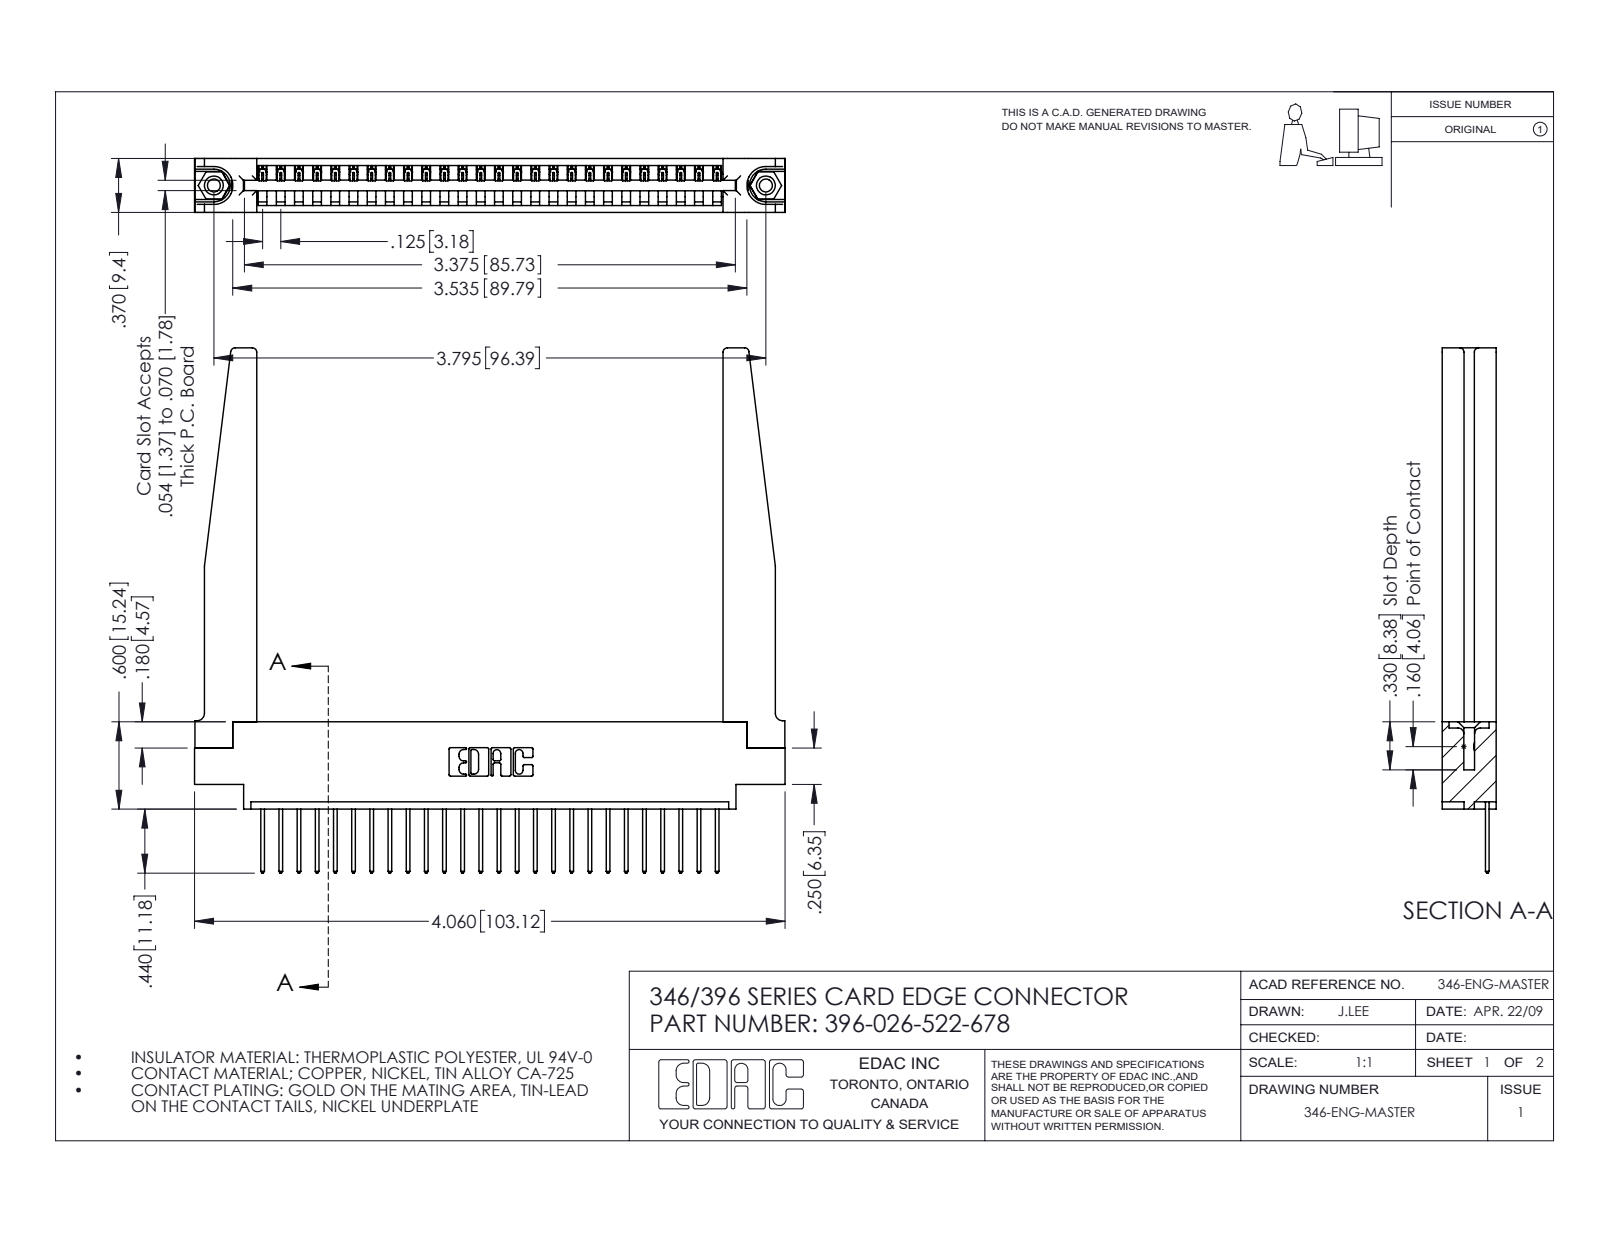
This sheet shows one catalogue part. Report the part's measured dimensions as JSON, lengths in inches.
{"part_name": "345-250-001_345-250-001-102; 346-220-078_345-220-078; 396-026-522-678; 345-292-001_345-293-122 (+1 more)", "step_written_by": "SolidWorks 2016 (CONFIG_CONTROL_DESIGN)", "units": "inches", "bodies": {"solids": 31, "faces": 1868, "planar": 1262, "cylindrical": 554, "other": 52}, "overall_size": [4.06, 3.61, 0.37], "volume_in3": 1.008, "surface_area_in2": 28.88, "round_holes": [[0.089, 2], [0.125, 2], [0.156, 2], [0.064, 1]], "round_bosses_or_shafts": [[0.155, 2]], "partial_cylinders_radius": [[0.006, 52], [0.01, 52], [0.01, 22], [0.03, 8], [0.007, 6], [0.031, 6], [0.026, 3], [0.031, 2]], "face_to_face_distances": [0.37, 0.048, 0.322, 0.072, 0.148, 0.15, 0.25, 0.298, 0.025, 0.222], "hole_center_spacings": [0.246, 3.587, 3.795]}
